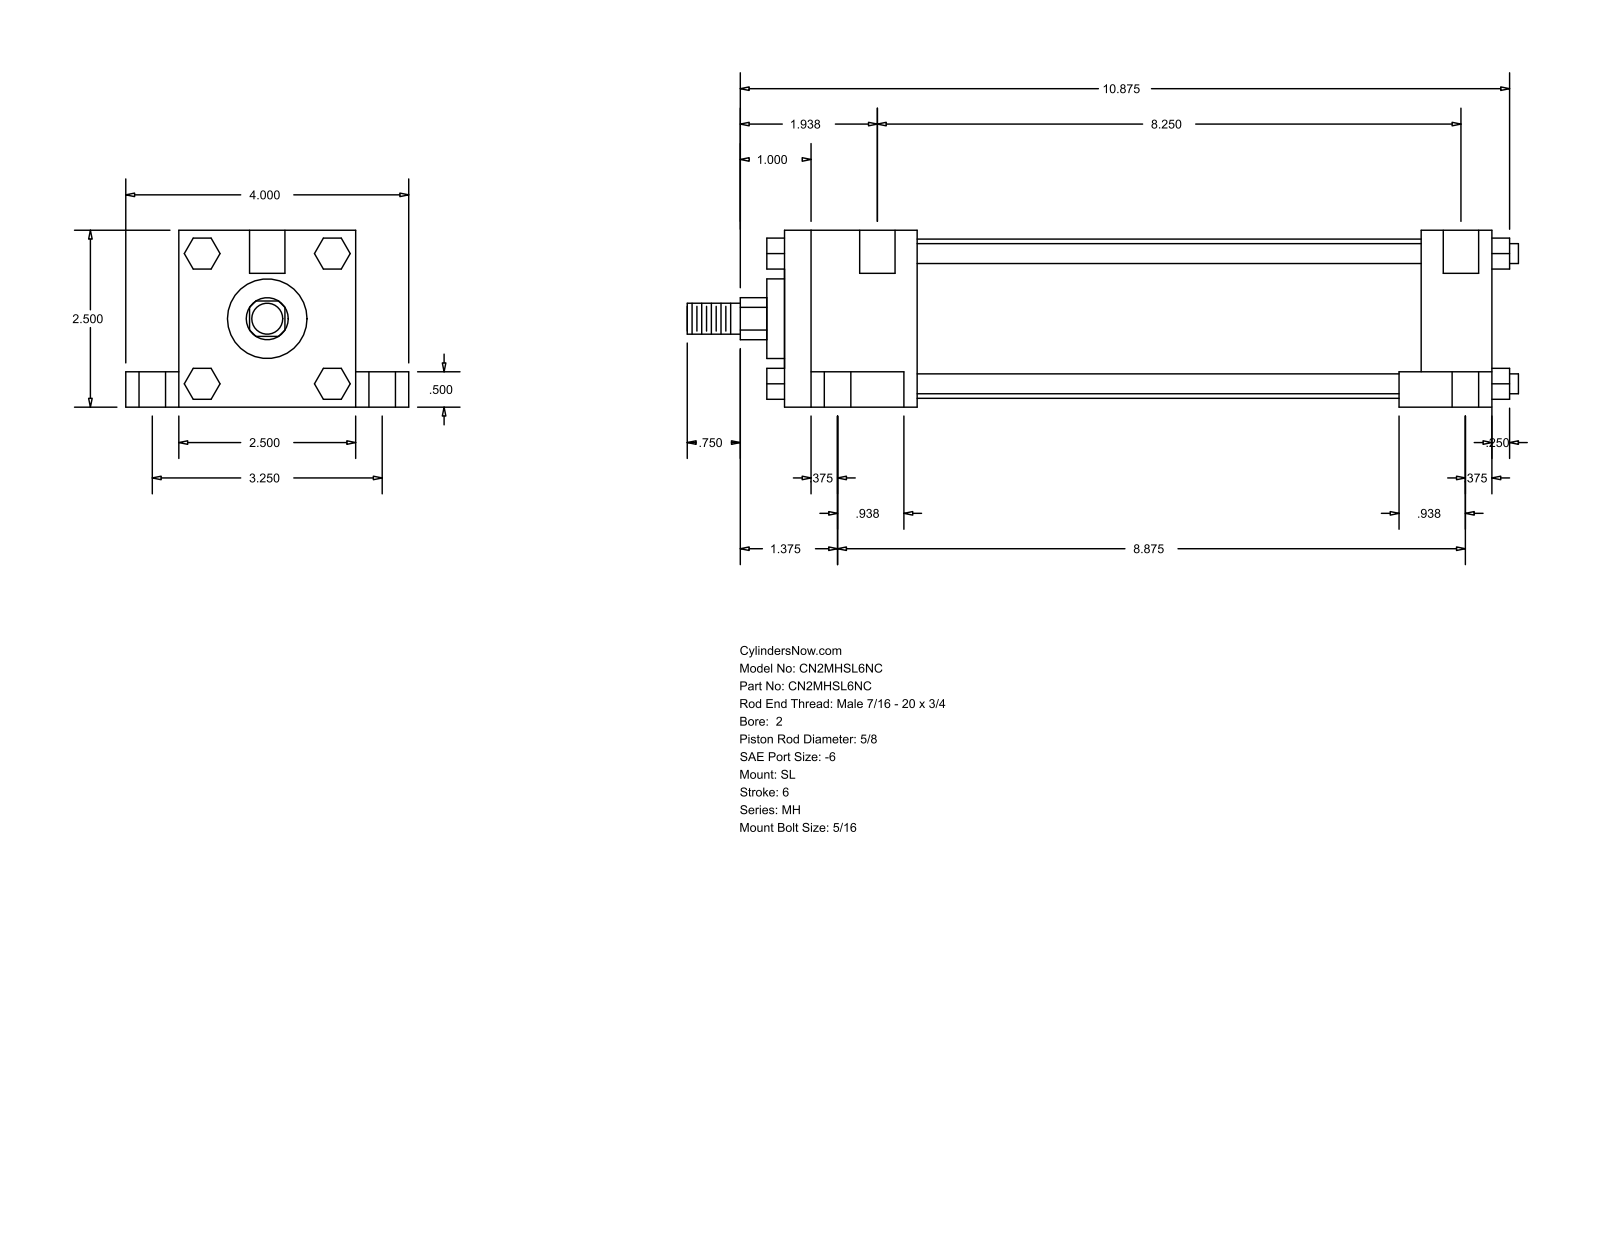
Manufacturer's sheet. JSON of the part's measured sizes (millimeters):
{"part_name": "MH_SL__0200_0.625", "step_written_by": "GSSL Pune (CONFIG_CONTROL_DESIGN)", "units": "millimeters", "bodies": {"solids": 0, "faces": 148, "planar": 112, "cylindrical": 36, "other": 0}, "overall_size": [298.45, 101.6, 63.5], "round_holes": [[5.56, 4], [9.53, 4], [15.88, 4], [12.7, 2]], "round_bosses_or_shafts": [[7.14, 4], [57.15, 1], [28.57, 1], [15.88, 1], [11.11, 1]], "partial_cylinders_radius": [[7.54, 1]], "face_to_face_distances": [63.5, 254, 12.7, 19.05, 82.55, 50.8, 228.59, 25.41, 47.62, 180.97], "hole_center_spacings": [41.3, 42.36, 43.67, 82.54, 215.14, 217.49, 219.81, 225.43]}
